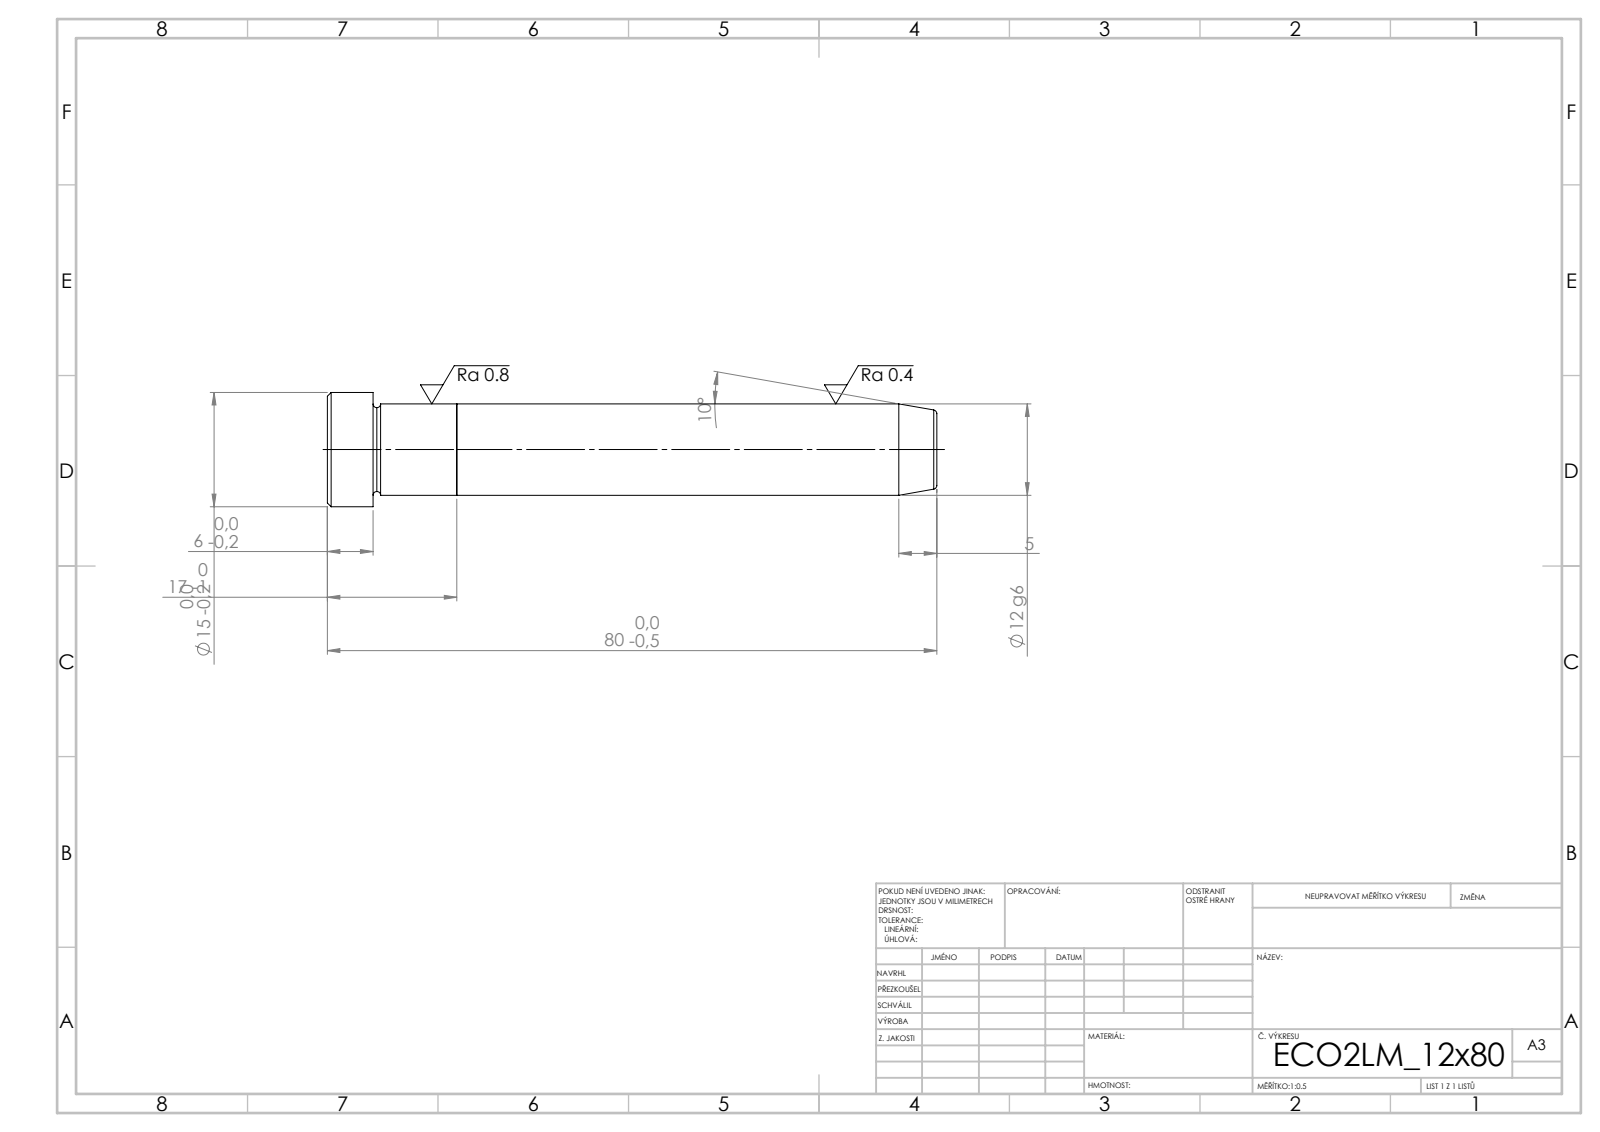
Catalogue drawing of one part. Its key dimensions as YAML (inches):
step_written_by: "SolidWorks 2019 (CONFIG_CONTROL_DESIGN)"
units: inches
bodies: {solids: 2, faces: 21, planar: 5, cylindrical: 6, other: 10}
overall_size: [3.15, 0.591, 0.591]
volume: 0.569
surface_area: 5.596
round_bosses_or_shafts:
  - {diameter: 0.591, count: 1}
  - {diameter: 0.472, count: 1}
face_to_face_distances: [0.669, 2.48, 3.15, 2.913, 0.433, 0.236]
